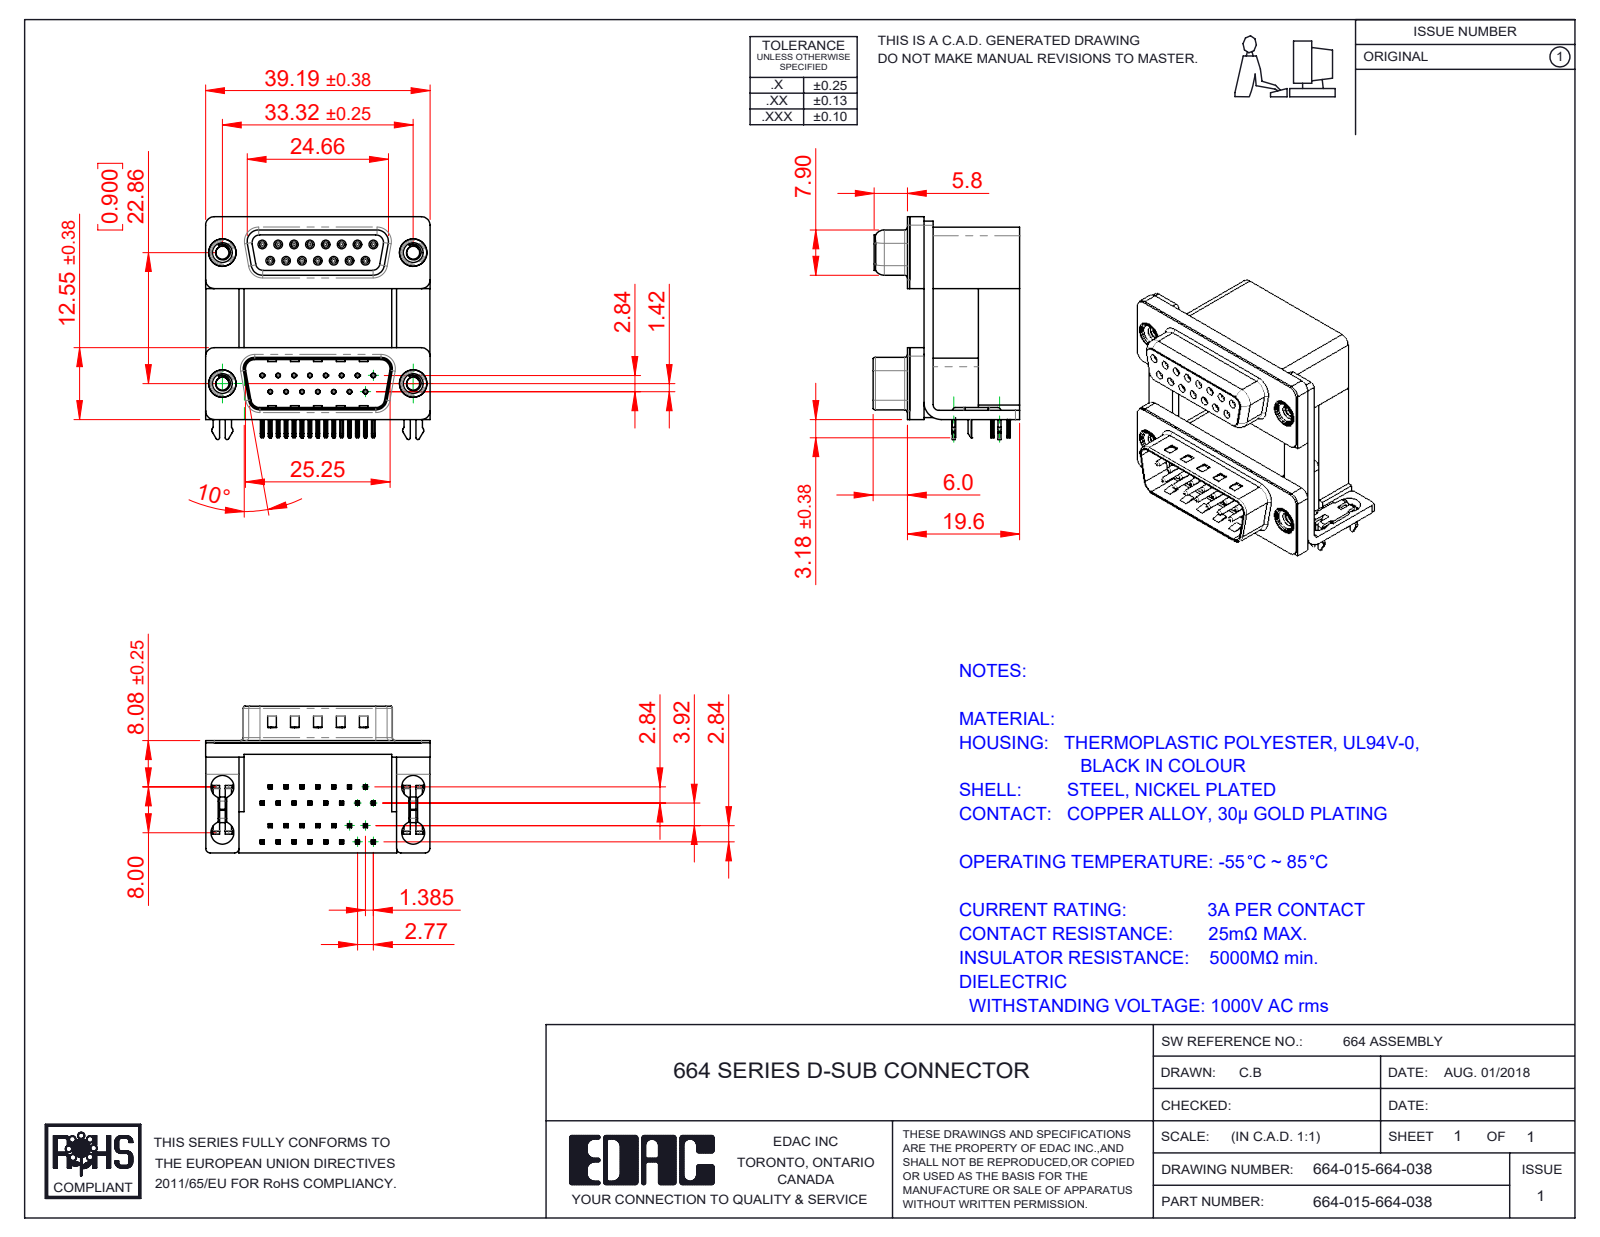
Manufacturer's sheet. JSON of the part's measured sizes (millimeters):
{"part_name": "664-015-664-038; 664 Contact Top Upper_H; 664 Housing Lower_15 Contacts; 664 Threaded Rivet_4-40 (+8 more)", "step_written_by": "SolidWorks 2020 (CONFIG_CONTROL_DESIGN)", "units": "millimeters", "bodies": {"solids": 43, "faces": 4064, "planar": 2117, "cylindrical": 1064, "other": 883}, "overall_size": [39.19, 38.91, 25.6], "volume_mm3": 15949, "surface_area_mm2": 17800, "round_holes": [[0.8, 30], [0.35, 15], [0.9, 15], [4, 8], [2.26, 4], [3.5, 4], [4.8, 4], [5, 4]], "round_bosses_or_shafts": [[1.2, 15], [0.75, 15], [4.9, 4], [4.75, 4], [3.9, 4]], "partial_cylinders_radius": [[0.1, 122], [0.25, 70], [0.15, 60], [0.12, 30], [0.35, 30], [0.5, 16], [1.5, 16], [0.34, 15]], "face_to_face_distances": [0.4, 19.2, 12, 7.2, 16.7, 9.5, 2.5, 2.19, 12.4, 22.86], "hole_center_spacings": [3.16, 2.77, 23.03, 5.54, 23.52, 8.31, 22.86, 24.32]}
